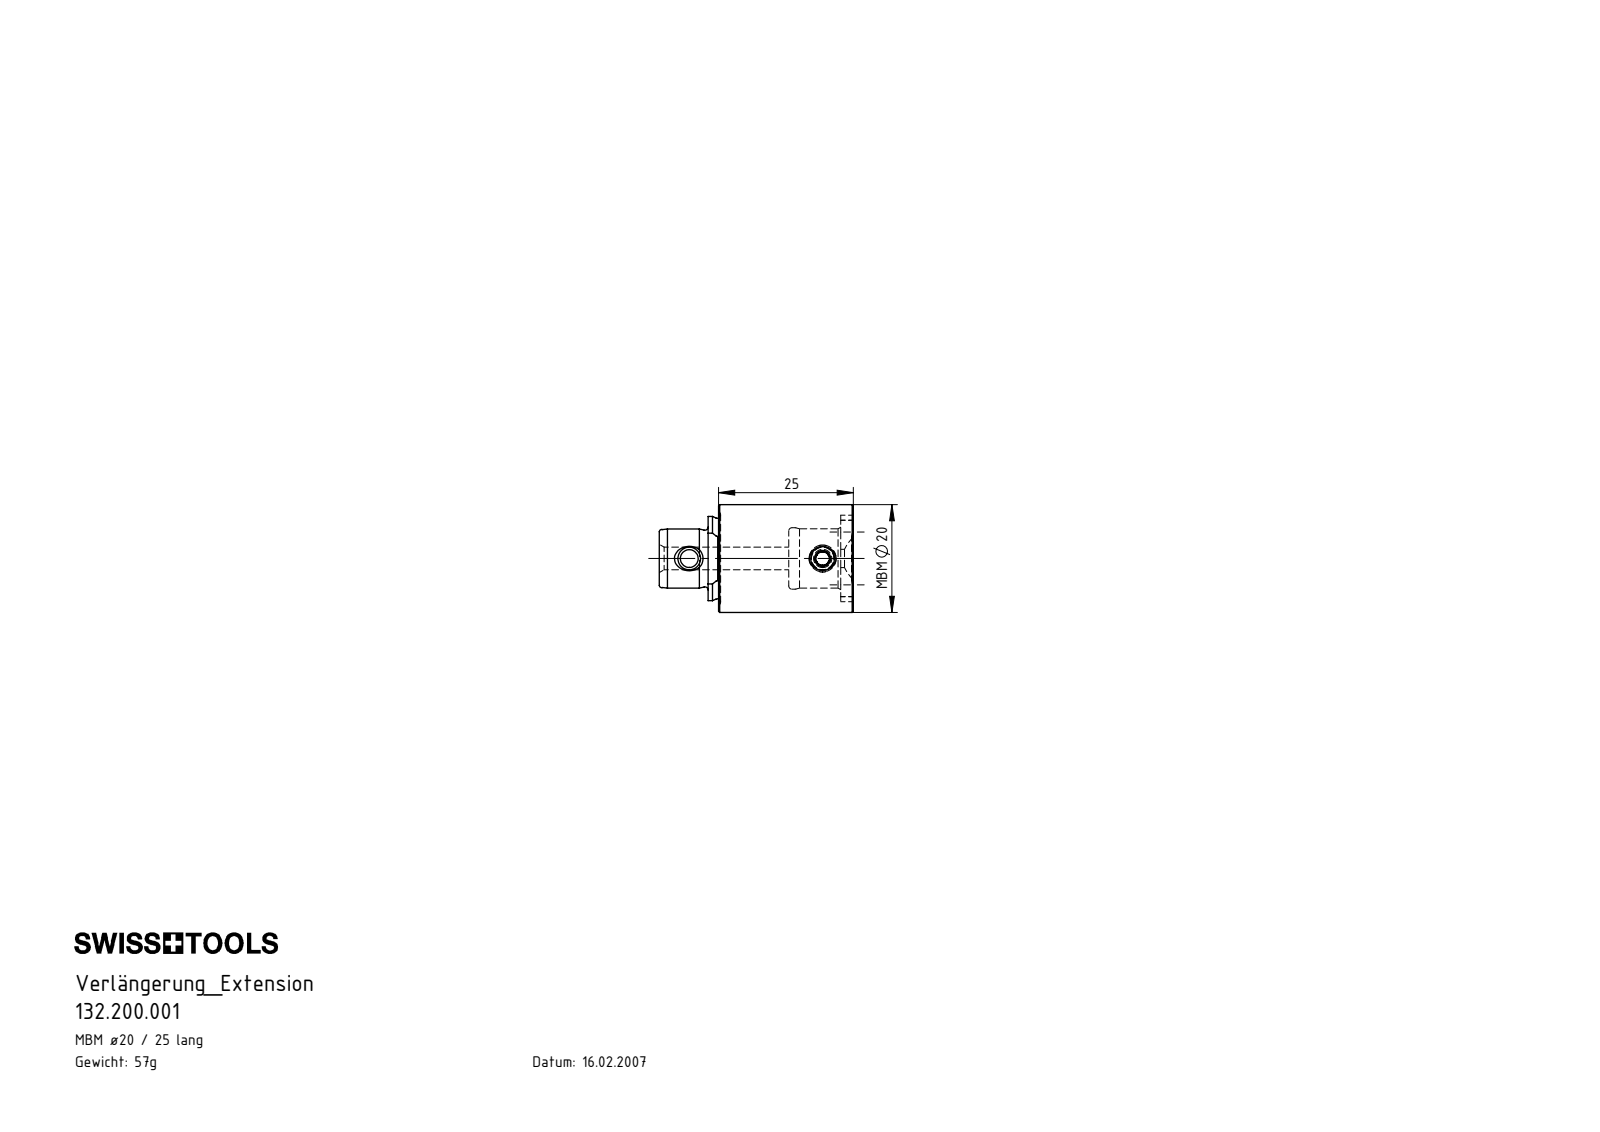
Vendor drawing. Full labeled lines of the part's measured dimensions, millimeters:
Part name (STEP PRODUCT): MB1.MB1.K01.025; MB1-ER1.001.006_A; MB1-MB1.K01.025_B
STEP written by: SolidWorks 2012 (CONFIG_CONTROL_DESIGN)
Units: millimetres
Bodies: 2 solids, 120 faces (24 planar, 30 cylindrical, 66 other)
Overall size (bounding box): 36 × 20 × 20
Volume: 7 282 mm³ · Surface area: 3 500 mm²
Round holes (diameter × count): ⌀4.2 ×2, ⌀3.3 ×1, ⌀11 ×1, ⌀11.4 ×1
Round bosses / shafts (diameter × count): ⌀20 ×1, ⌀5 ×1
Partial cylindrical surfaces — rounded edges, fillets, slot ends (radius × count): R2.2 ×4, R6.5 ×1, R7.83 ×1, R8.03 ×1
Main face-to-face distances: 2.35, 9.65, 12, 14.95, 24.6, 26.95, 9.05, 24, 33.65, 36
Hole centre spacings: 24.75
